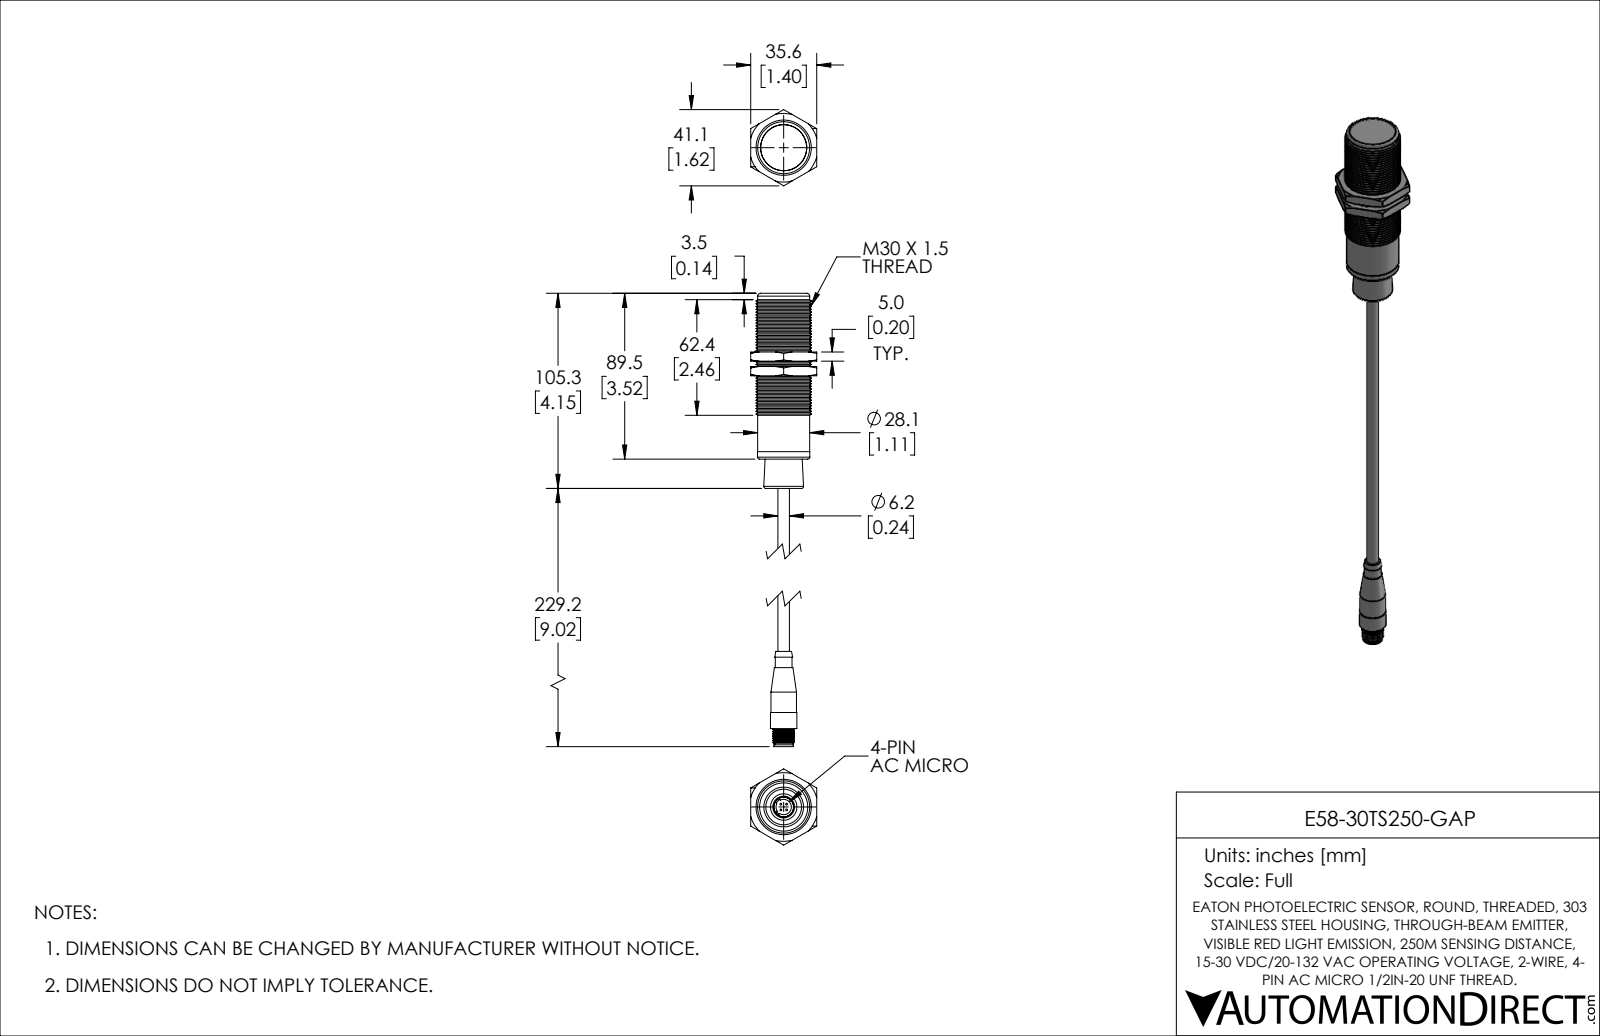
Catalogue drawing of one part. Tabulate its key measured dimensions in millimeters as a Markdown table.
| quantity | value |
| --- | --- |
| part name | E58-30TS250-GAP |
| STEP written by | SolidWorks 2021 (AUTOMOTIVE_DESIGN) |
| units | millimeters |
| bodies | 3 solids, 228 faces (46 planar, 25 cylindrical, 157 other) |
| overall size | 334.5 × 41.1 × 35.6 |
| volume | 78 100 mm³ |
| surface area | 24 090 mm² |
| round holes (diameter × count) | 1.8 × 2, 1 × 1, 6.4 × 1, 8.3 × 1, 24.8 × 1 |
| round bosses / shafts (diameter × count) | 1 × 3, 28.2 × 1, 28.1 × 1, 14.3 × 1, 13.8 × 1, 11.7 × 1, 10.6 × 1, 9.5 × 1 |
| partial cylindrical surfaces (radius × count) | 4.6 × 1 |
| main face-to-face distances | 7.8, 5, 43.8, 36, 35.6, 38.9, 2.9, 31, 12.8, 88.8 |
| hole center spacings | 2.2, 3.4, 4.5, 4.5, 6.2, 9 |
